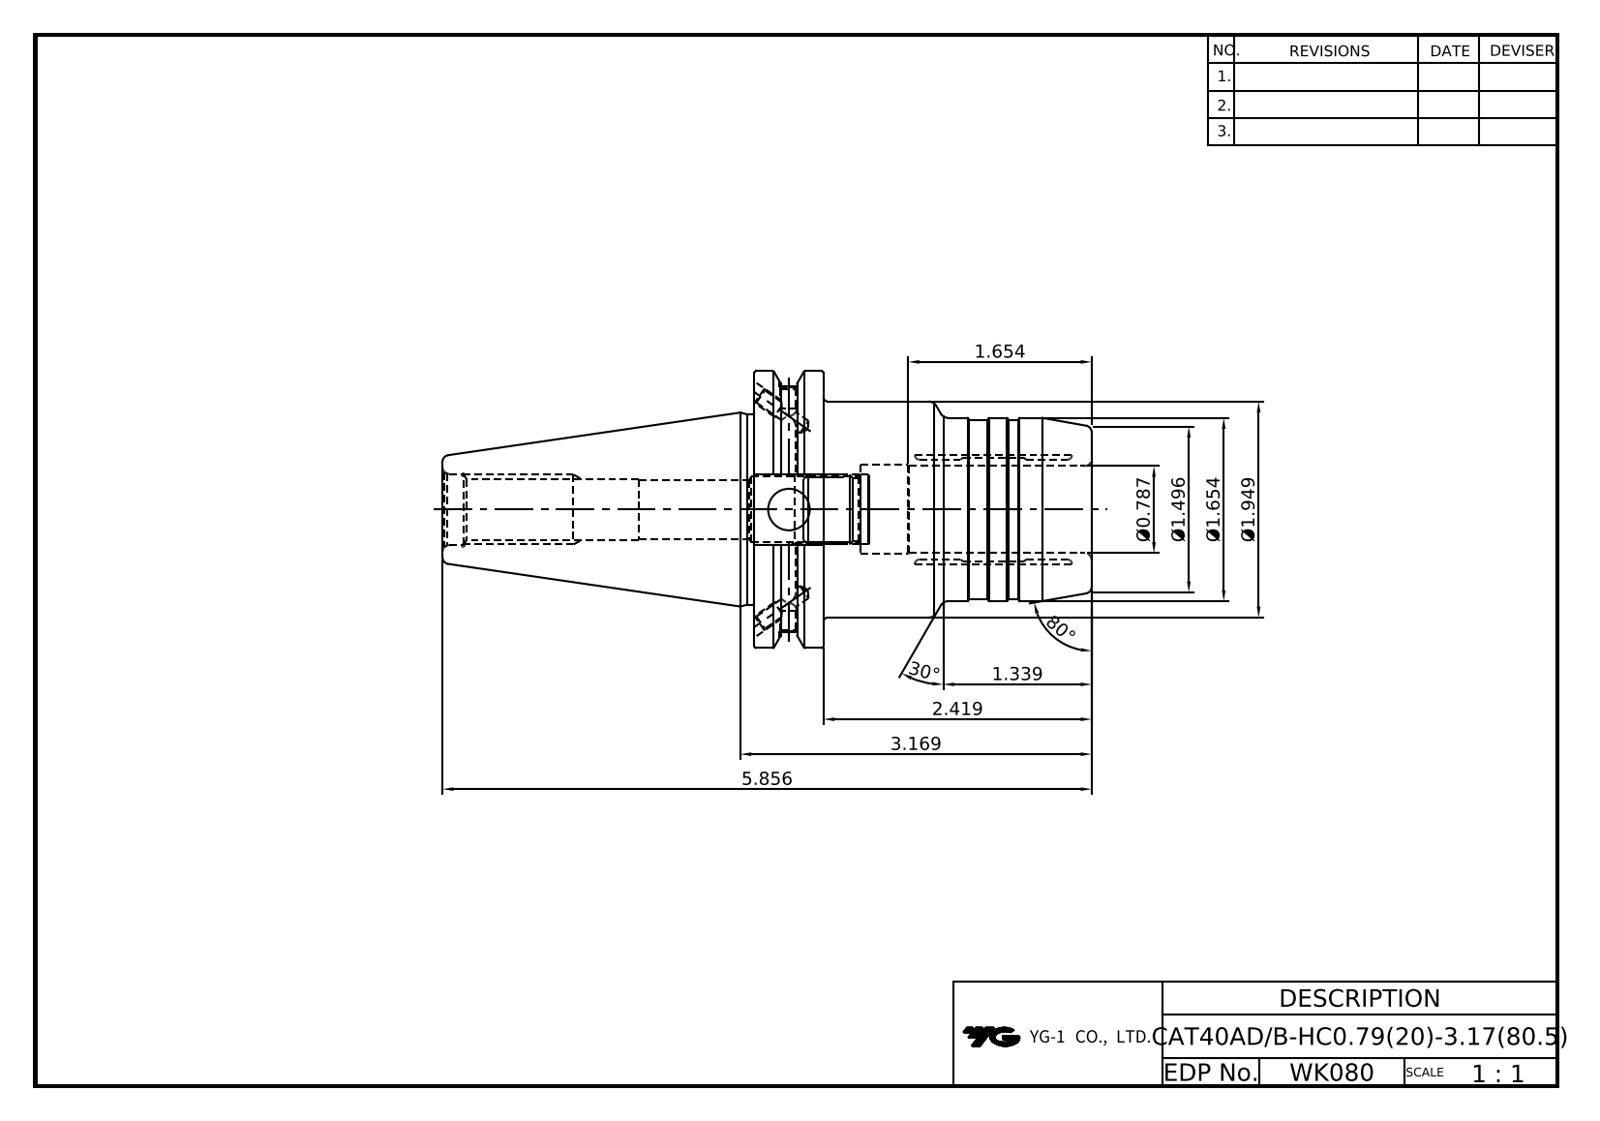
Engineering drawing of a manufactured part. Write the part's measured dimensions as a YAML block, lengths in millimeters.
part_name: "LO-CAT40ADB-HC20-80.5"
step_written_by: "Autodesk Inventor 2025 (AUTOMOTIVE_DESIGN)"
units: millimeters
bodies: {solids: 1, faces: 106, planar: 34, cylindrical: 35, other: 37}
overall_size: [148.75, 63.5, 61.09]
volume: 179110
surface_area: 32668
round_holes:
  - {diameter: 3.24, count: 4}
  - {diameter: 4, count: 2}
  - {diameter: 4.2, count: 2}
  - {diameter: 9.53, count: 1}
  - {diameter: 13, count: 1}
  - {diameter: 13.39, count: 1}
  - {diameter: 14.92, count: 1}
  - {diameter: 16.3, count: 1}
  - {diameter: 20, count: 1}
  - {diameter: 20.4, count: 1}
round_bosses_or_shafts:
  - {diameter: 63.5, count: 1}
  - {diameter: 49.5, count: 1}
  - {diameter: 43.6, count: 1}
  - {diameter: 42, count: 1}
  - {diameter: 41, count: 1}
partial_cylinders:
  - {radius: 8.19, count: 1}
  - {radius: 28.15, count: 1}
face_to_face_distances: [15.88, 77.33, 61.45, 47.6, 16.38, 24.33, 8.45, 53, 71.42, 87.3]
